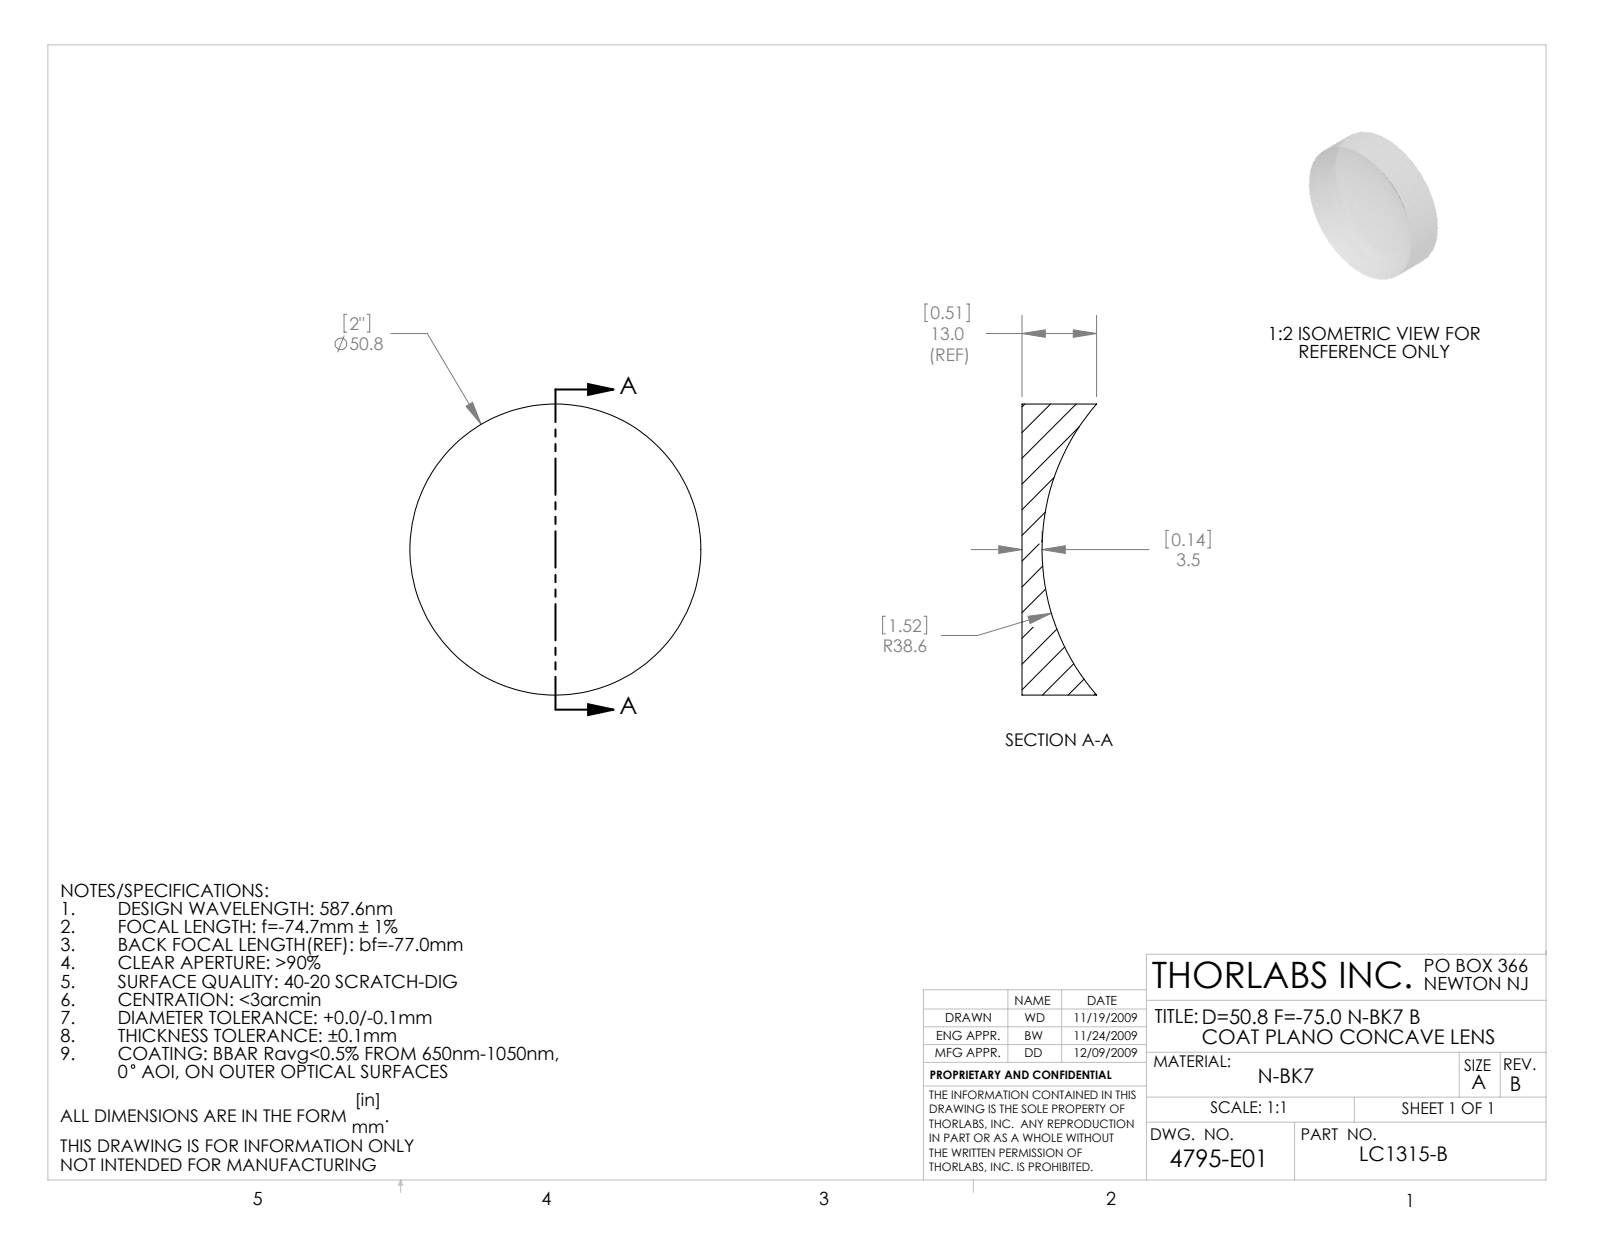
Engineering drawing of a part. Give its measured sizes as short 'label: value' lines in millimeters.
name: 4795-E0W
written by: SolidWorks 2009 (AUTOMOTIVE_DESIGN)
unit: mm
bodies: 1 solid, 5 faces (1 planar, 2 cylindrical, 2 other)
size: 50.8 × 50.8 × 13.04
volume: 16 305 mm³; area: 6 420 mm²
bosses: 1× ⌀50.8
